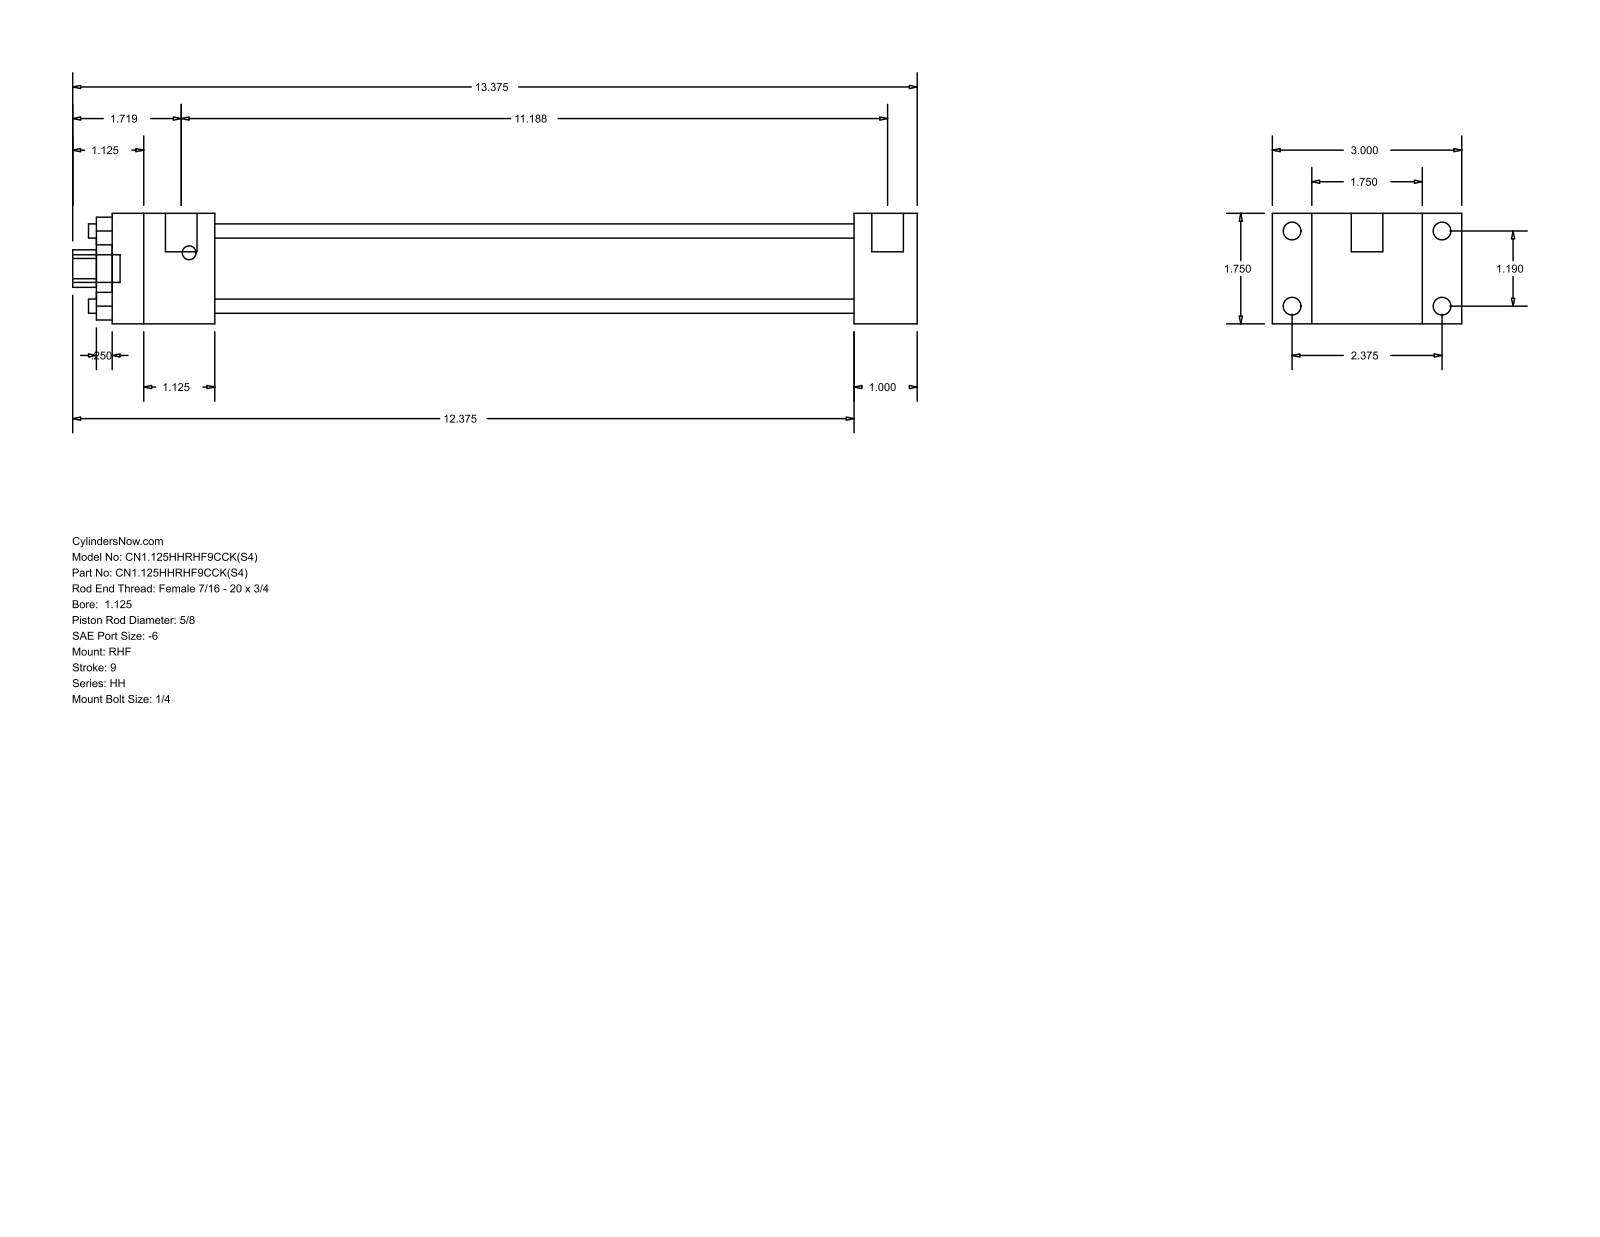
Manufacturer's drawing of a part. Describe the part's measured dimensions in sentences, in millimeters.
The part is named "HH_RHF__0112_0.625". Its 3-D file was written by "GSSL Pune (CONFIG_CONTROL_DESIGN)". It is 0 solids with 88 faces: 60 planar, 28 cylindrical and 0 other. Overall it measures 339.73 by 76.2 by 44.45 millimeters. Round holes: 4 of diameter 5.71, 1 of diameter 15.88, 1 of diameter 28.57, 1 of diameter 34.92. Round bosses or shafts: 4 of diameter 7.14, 4 of diameter 5.56, 2 of diameter 12.7, 1 of diameter 11.11. Partial cylindrical surfaces (rounded edges, fillets, slot ends): 1 of radius 7.54. The main face-to-face distances are 44.46, 15.87, 60.33, 25.41, 76.2, 257.17, 282.58, 41.27, 298.44, 323.85. The hole center spacings are 21.37, 30.22, 42.74.
